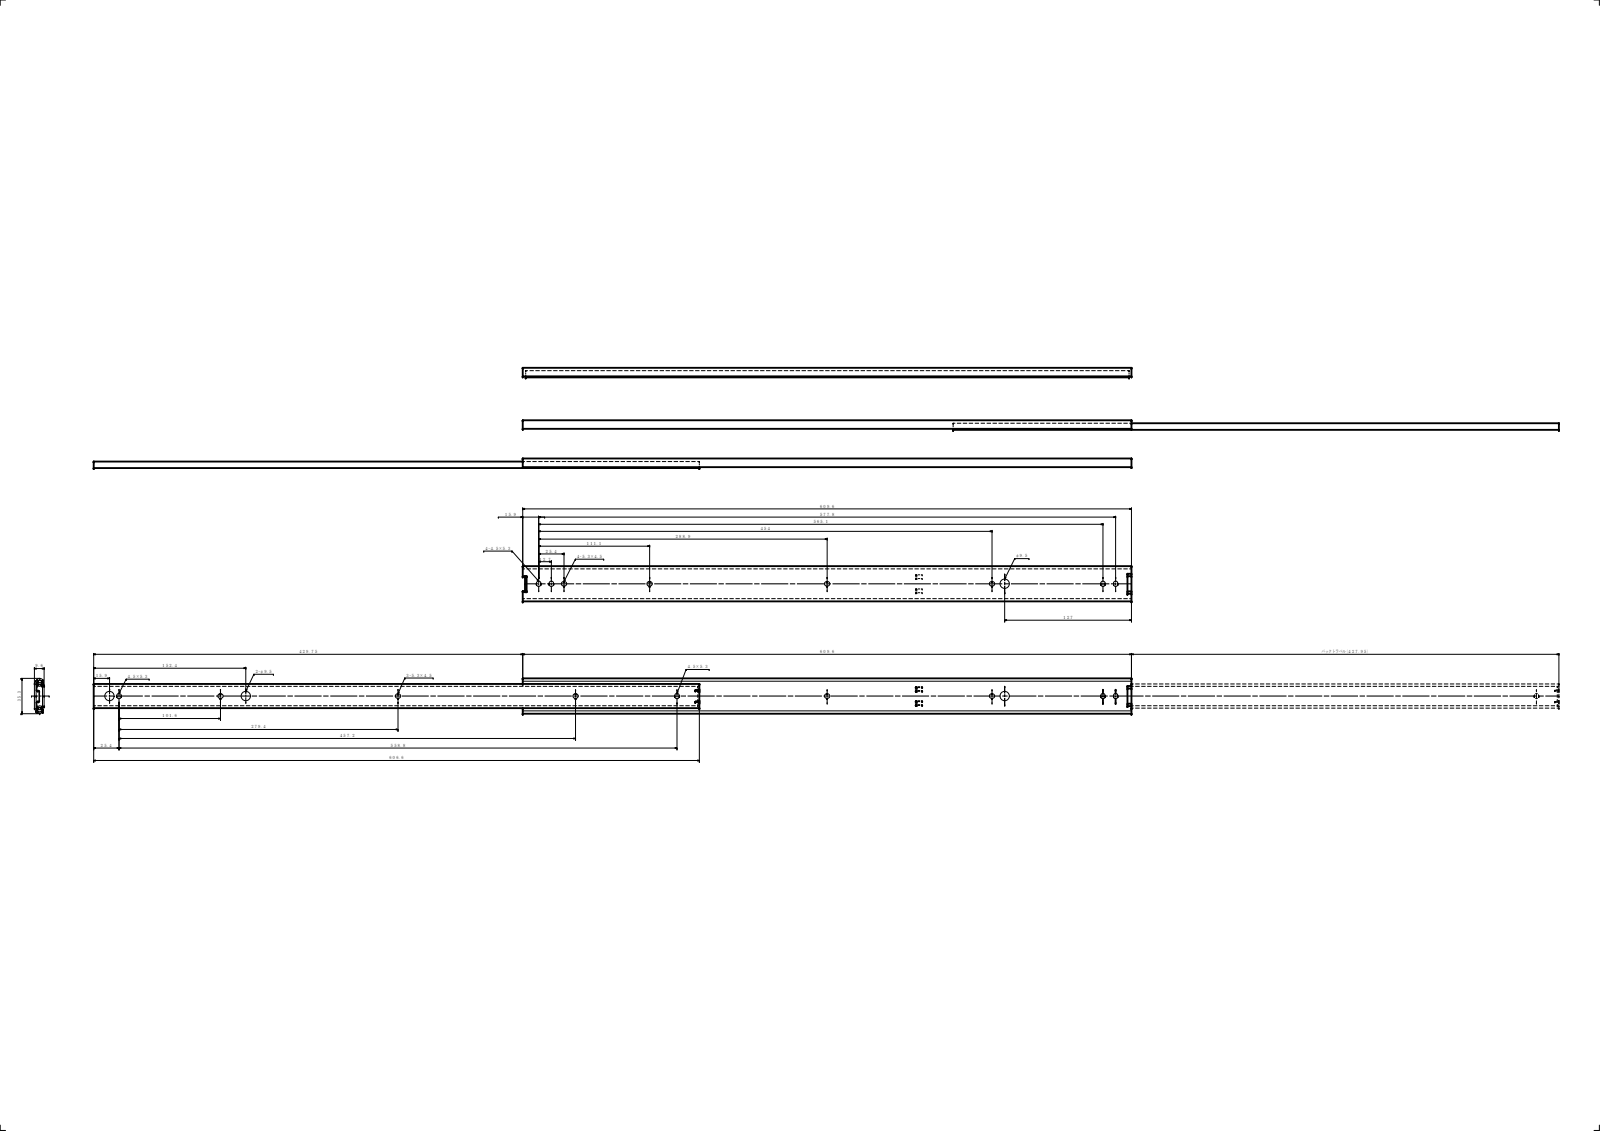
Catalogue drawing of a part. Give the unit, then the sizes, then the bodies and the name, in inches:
Units: inches
Overall size (bounding box): 40.919 × 1.39 × 0.378
Round holes (diameter × count): ⌀0.374 ×3
Partial cylindrical surfaces — rounded edges, fillets, slot ends (radius × count): R0.089 ×26, R0.016 ×6, R0.039 ×4, R0.098 ×4, R0.118 ×4, R0.008 ×2, R0.071 ×2, R0.079 ×2
Main face-to-face distances: 0.063, 0.315, 0.378, 0.252, 0.051, 0.264, 0.184, 0.121, 0.114, 0.201
Hole centre spacings: 5.374, 29.919, 35.293
Volume: 4.66 in³ · Surface area: 155.2 in²
Bodies: 2 solids, 147 faces (72 planar, 75 cylindrical, 0 other)
Part name (STEP PRODUCT): 3520-24; OM 3520-24; IM 3521-24
STEP written by: SolidWorks 2019 (CONFIG_CONTROL_DESIGN)
